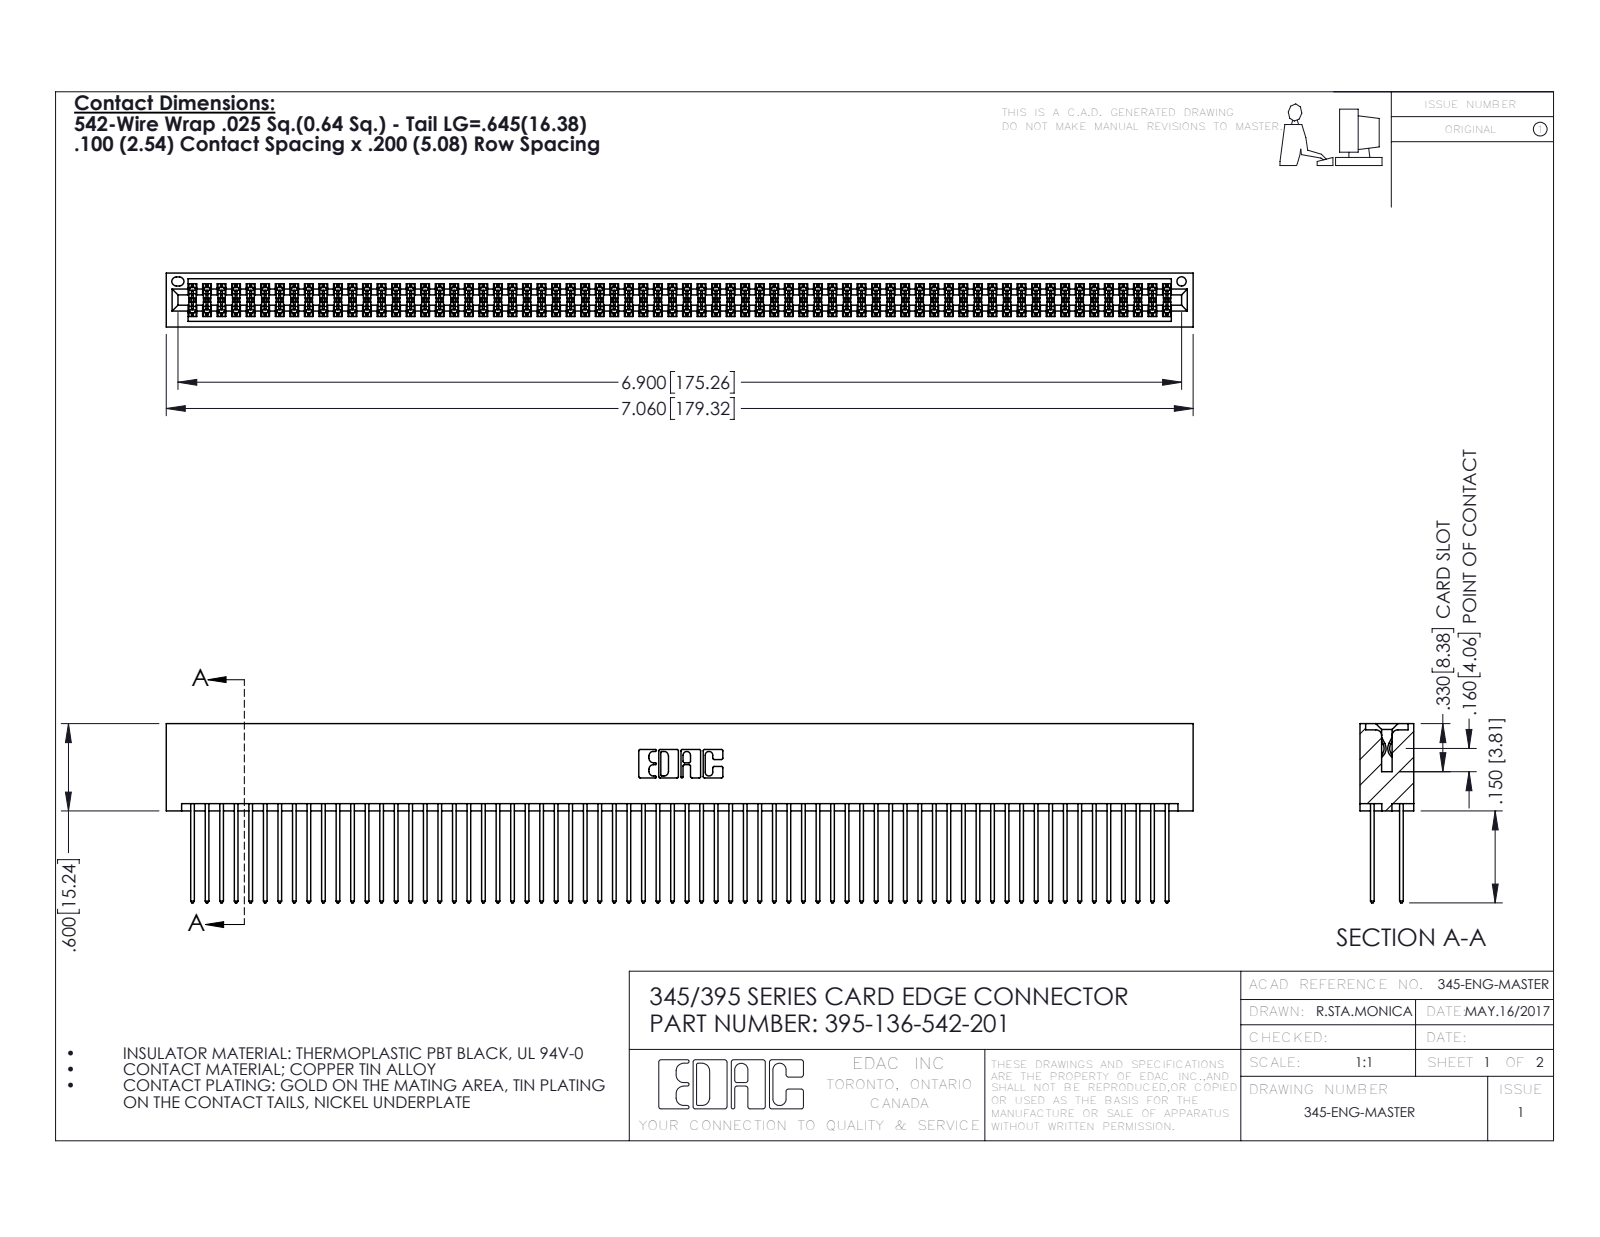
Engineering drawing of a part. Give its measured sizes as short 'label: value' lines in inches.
name: 345-292-001_345-293-142; 345 Part_No Mounting Lugs; 395-136-542-201
written by: SolidWorks 2016 (CONFIG_CONTROL_DESIGN)
unit: in
bodies: 137 solids, 6918 faces (4564 planar, 2354 cylindrical, 0 other)
size: 7.06 × 1.232 × 0.37
volume: 1.154 in³; area: 49.17 in²
holes: 1× ⌀0.064
rounds: 204× R0.006, 136× R0.01, 22× R0.01, 6× R0.007, 6× R0.031, 3× R0.026, 2× R0.014, 2× R0.019
face distances: 0.298, 0.072, 0.2, 0.098, 0.272, 0.025, 0.225, 0.37, 0.175, 0.149
